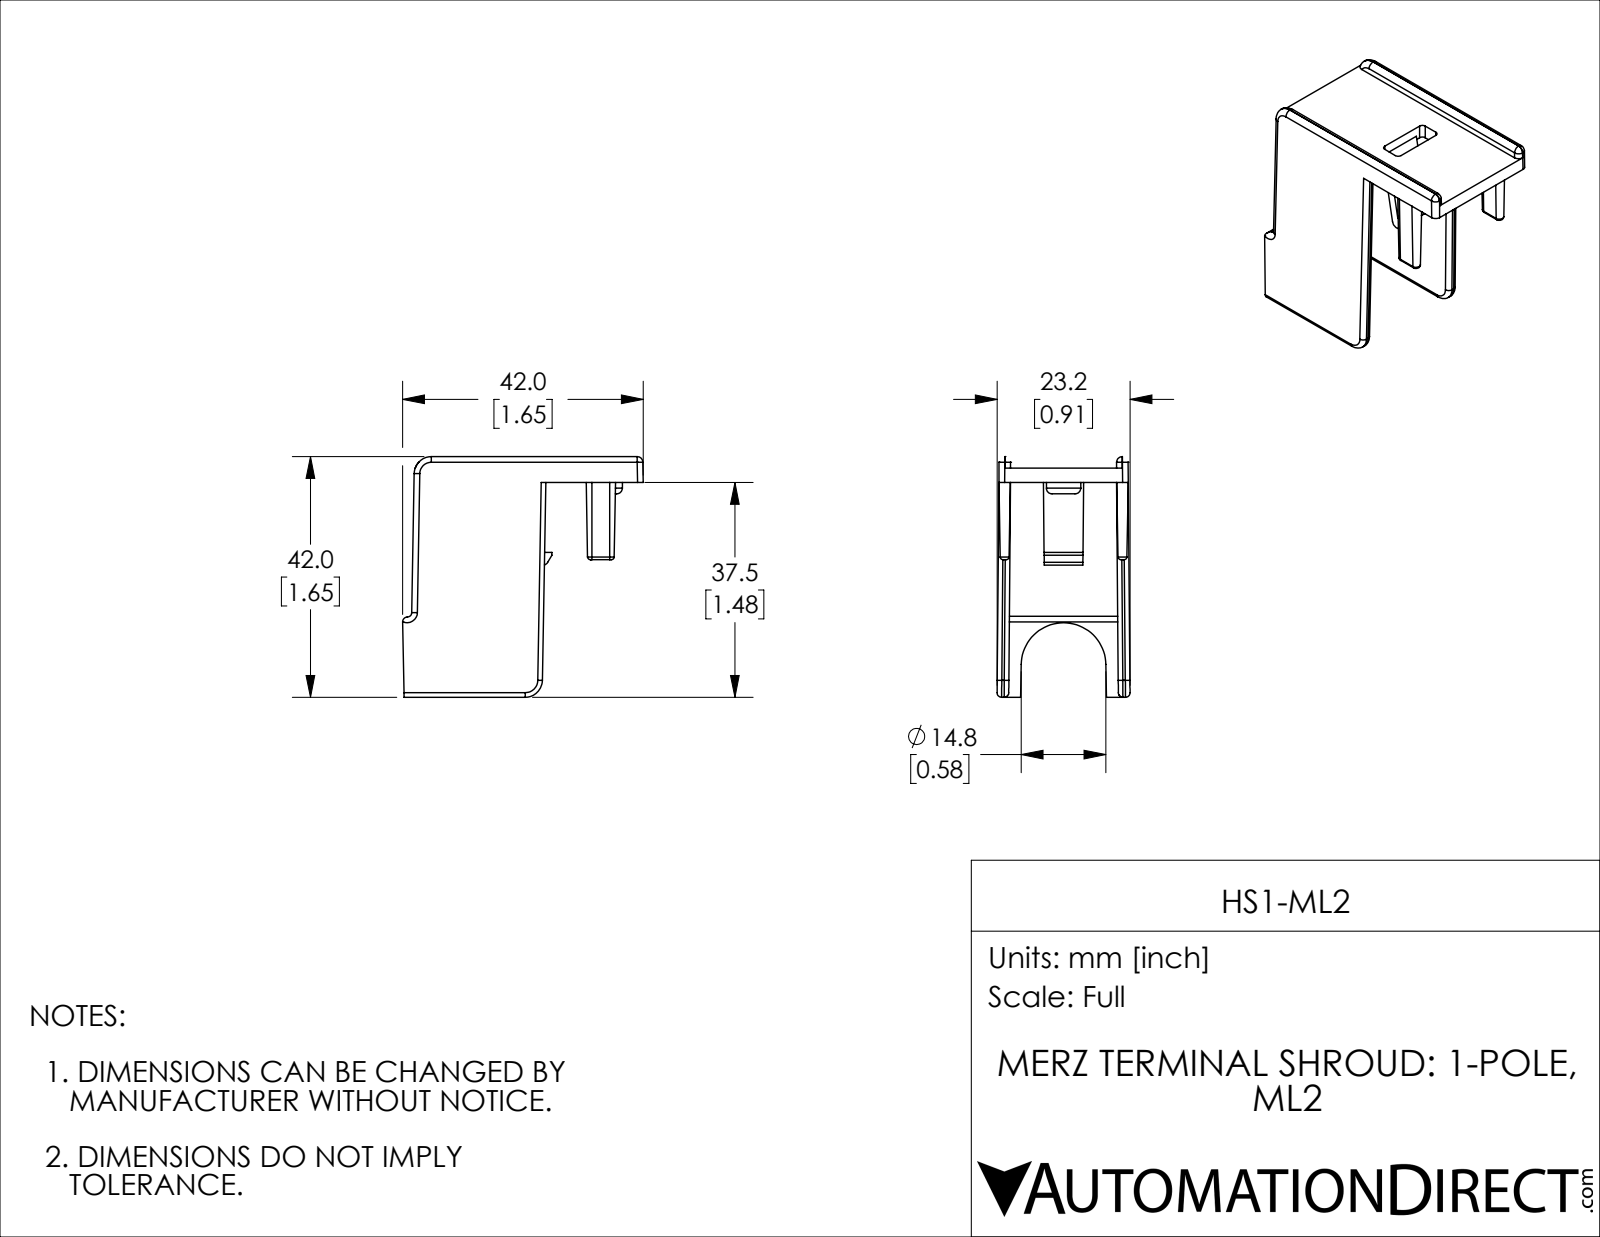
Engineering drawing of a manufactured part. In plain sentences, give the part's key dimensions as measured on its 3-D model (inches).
The part is named "HS1-ML2". Its 3-D file was written by "SolidWorks 2019 (AUTOMOTIVE_DESIGN)". It is 1 solid with 111 faces: 44 planar, 40 cylindrical and 27 other. Overall it measures 1.654 by 1.654 by 0.914 inches. Its volume is 0.475 cubic inches and its surface area 11.87 square inches. Round bosses or shafts: 1 of diameter 0.236. Partial cylindrical surfaces (rounded edges, fillets, slot ends): 10 of radius 0.031, 10 of radius 0.039, 4 of radius 0.02, 4 of radius 0.028, 3 of radius 0.039, 2 of radius 0.118, 1 of radius 0.291. The main face-to-face distances are 0.08, 0.098, 0.059, 0.078, 0.81, 0.728, 0.082, 1.67, 0.502, 0.582.
